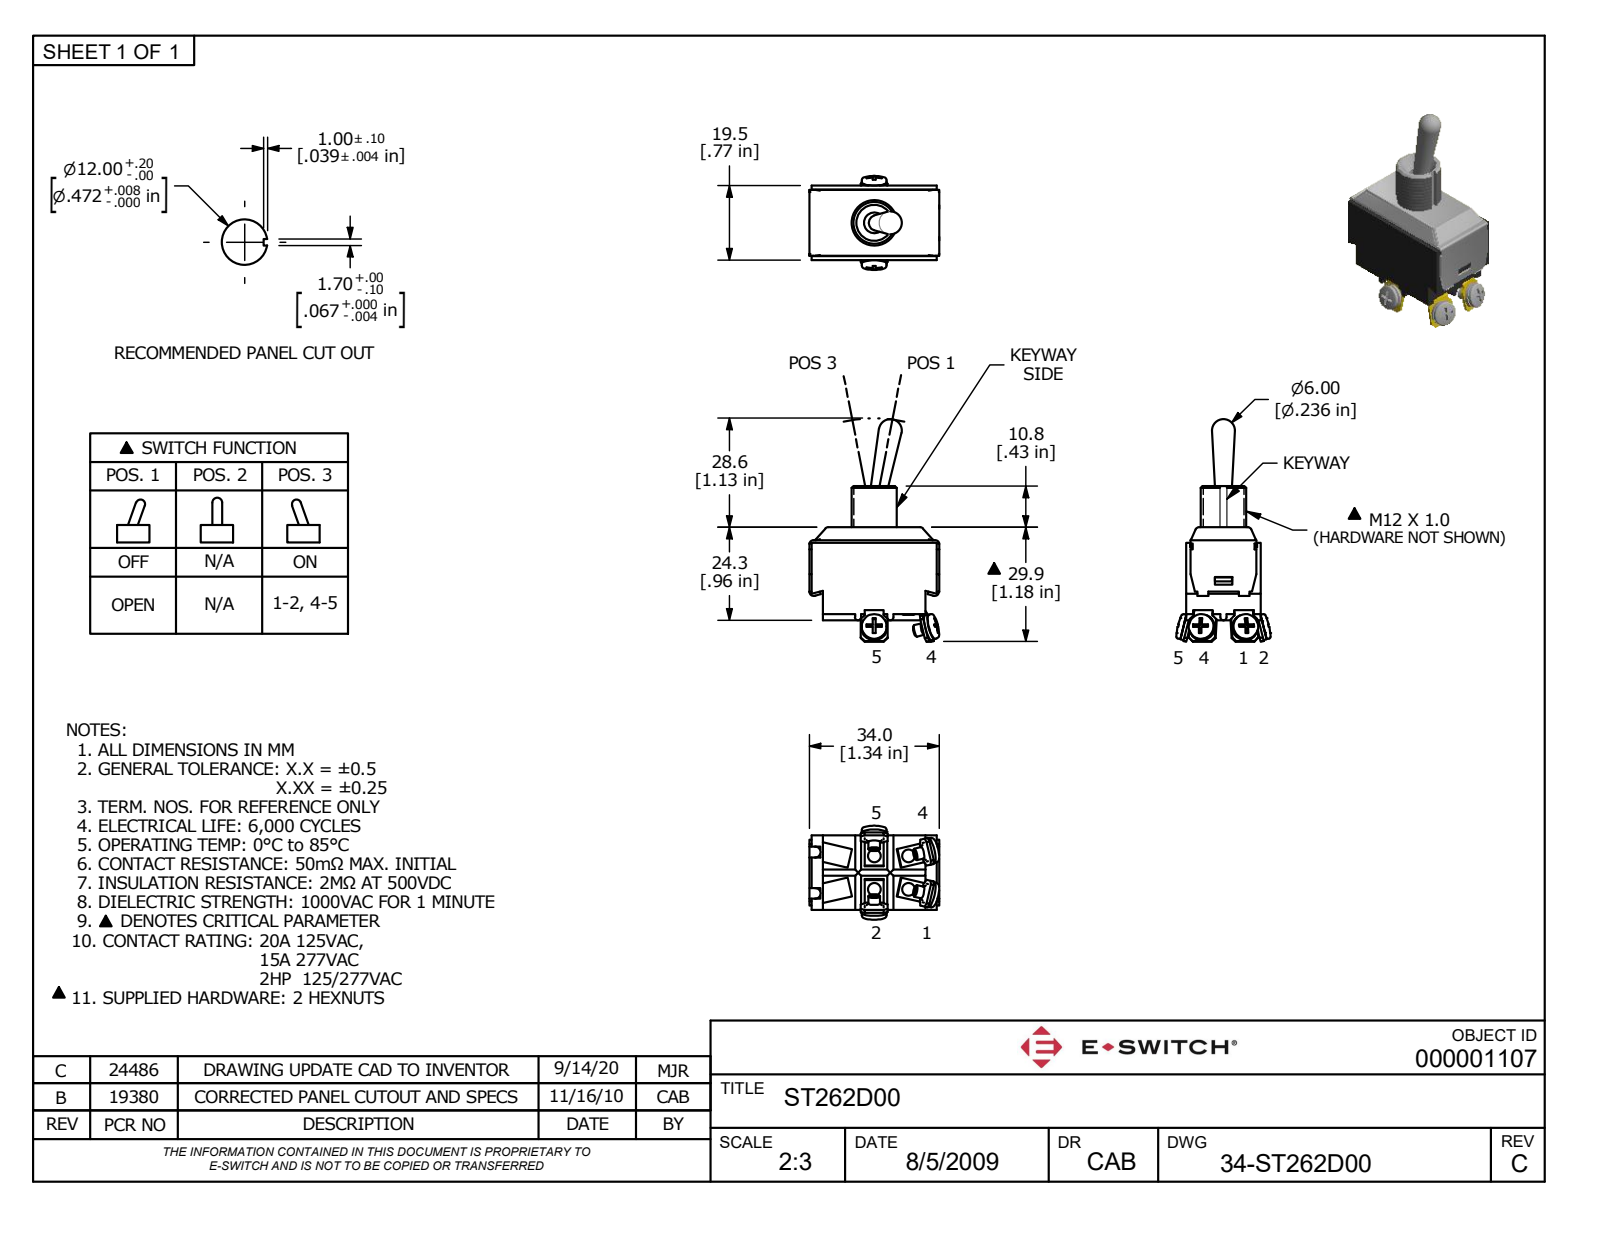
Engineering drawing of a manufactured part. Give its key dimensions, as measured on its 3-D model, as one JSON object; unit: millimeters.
{"part_name": "ST262D00", "step_written_by": "Autodesk Inventor 2022 (AUTOMOTIVE_DESIGN)", "units": "millimeters", "bodies": {"solids": 1, "faces": 436, "planar": 301, "cylindrical": 73, "other": 62}, "overall_size": [58.3, 34.02, 24.61], "volume_mm3": 15315, "surface_area_mm2": 5861, "round_holes": [[2, 4], [4, 1], [5.4, 1]], "round_bosses_or_shafts": [[6.73, 4], [6.53, 4], [3.1, 4], [11.91, 1]], "partial_cylinders_radius": [[1, 10], [1.1, 6], [0.25, 4], [1.4, 4], [0.8, 3], [0.2, 2], [0.3, 2], [0.6, 2]], "face_to_face_distances": [19.5, 3.6, 30.4, 34, 22.7, 0.8, 1, 21.7, 1.7, 18.4], "hole_center_spacings": [4.35, 8.7, 9, 10, 12.52]}
